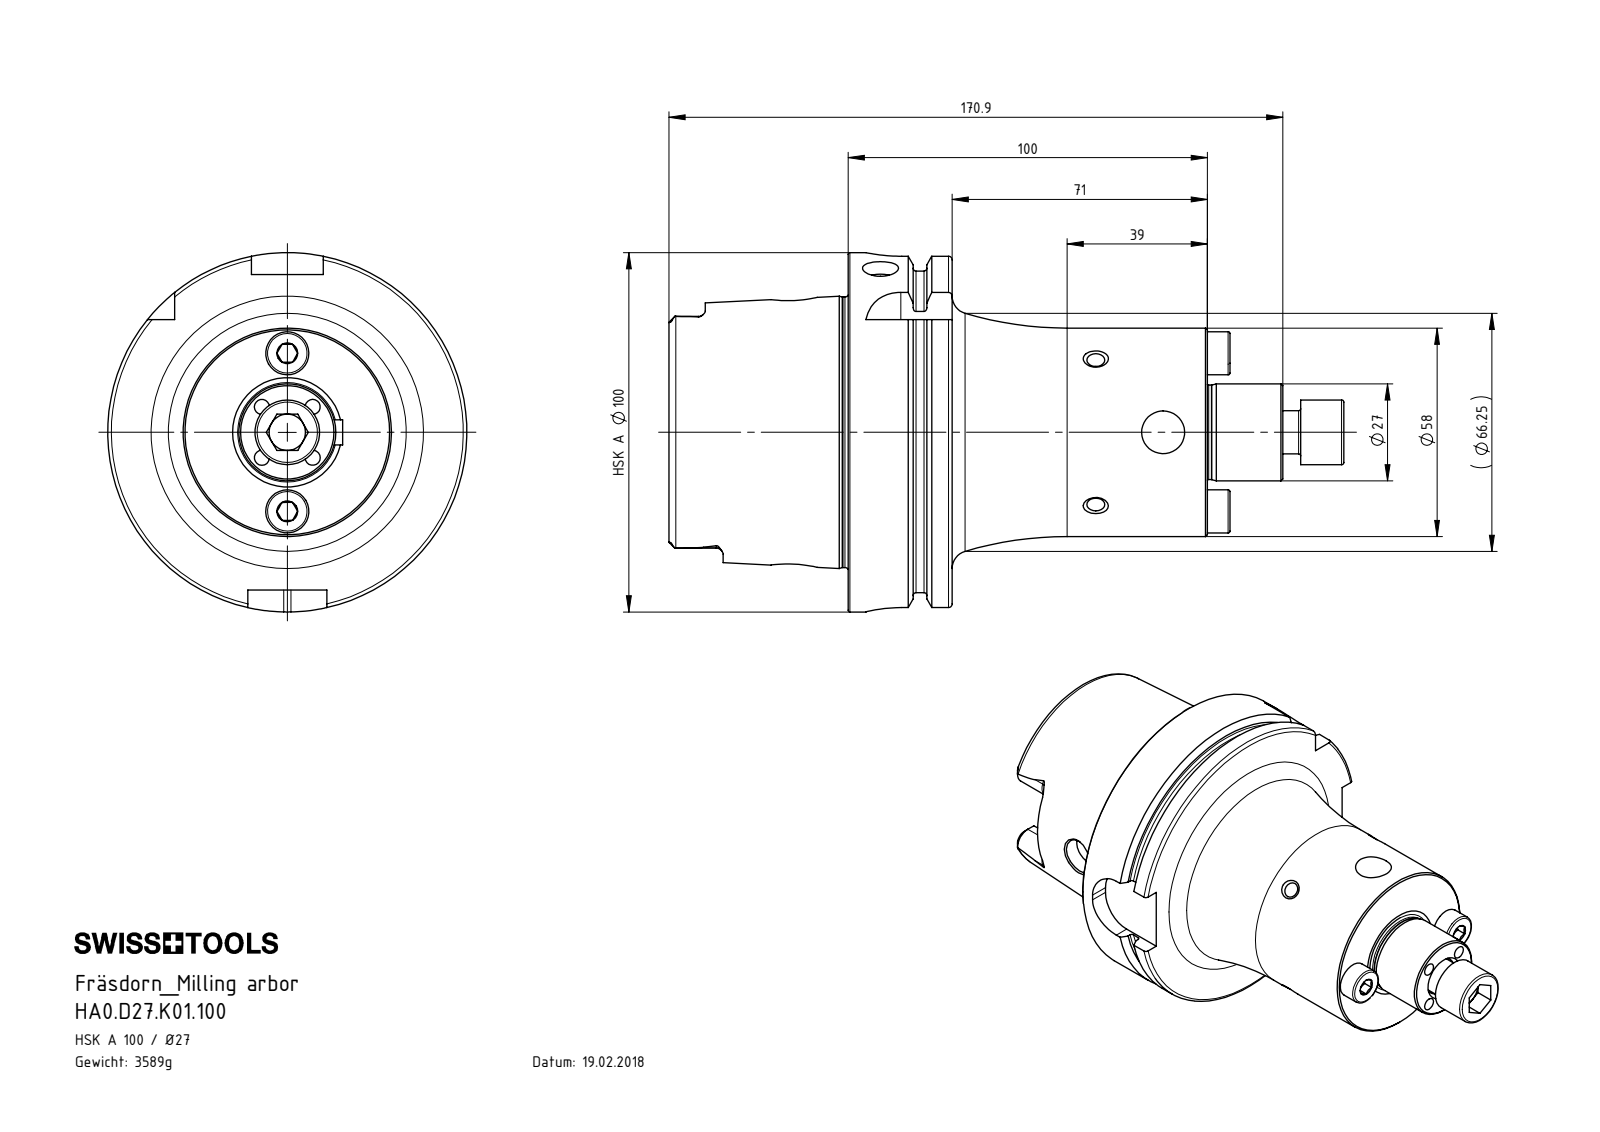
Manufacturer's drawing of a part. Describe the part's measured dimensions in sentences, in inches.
The part is named "D27-ER2.001.021_B; ISO 4762 - M12 x 30; HA0.D27.K01.100; HA0-D27.K01.100_D_Fertigbearbeitung (+1 more)". Its 3-D file was written by "SolidWorks 2017 (AUTOMOTIVE_DESIGN)". It is 5 solids with 369 faces: 89 planar, 118 cylindrical and 162 other. Overall it measures 7.398 by 3.937 by 3.937 inches. Its volume is 27.89 cubic inches and its surface area 117.4 square inches. Round holes: 6 of diameter 0.165, 6 of diameter 0.197, 5 of diameter 0.394, 2 of diameter 0.472, 1 of diameter 0.402, 1 of diameter 0.512, 1 of diameter 0.886, 1 of diameter 1.024, 1 of diameter 2.087, 1 of diameter 2.48. Round bosses or shafts: 2 of diameter 0.472, 2 of diameter 0.236, 2 of diameter 0.181, 1 of diameter 3.937, 1 of diameter 3.62, 1 of diameter 2.963, 1 of diameter 2.283, 1 of diameter 1.063. Partial cylindrical surfaces (rounded edges, fillets, slot ends): 6 of radius 0.075, 4 of radius 0.192, 4 of radius 0.394, 2 of radius 0.138, 2 of radius 0.157. The main face-to-face distances are 1.14, 3.937, 2.797, 0.49, 0.65, 3.447, 1.965, 2.455, 3.104, 5.902. The hole center spacings are 0.394, 0.557, 0.65, 0.829, 1.178, 0.787, 0.866, 1.732.
